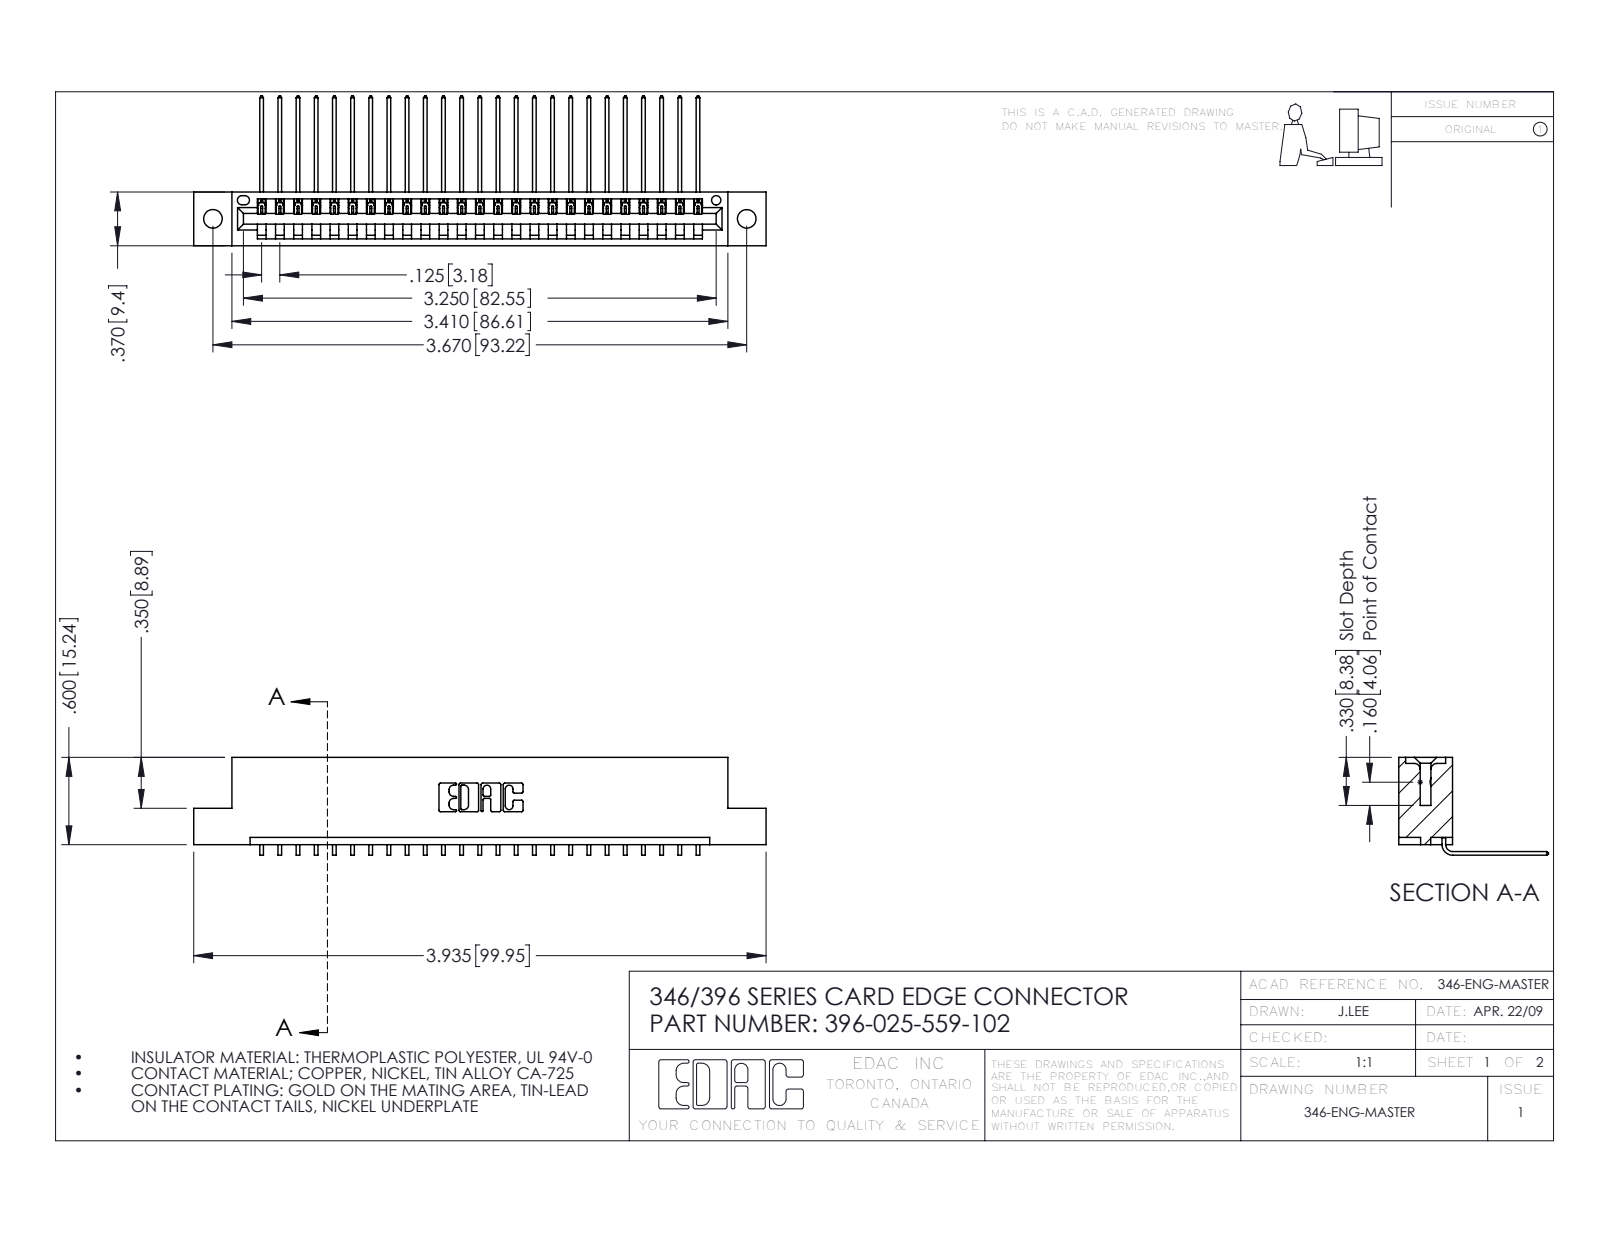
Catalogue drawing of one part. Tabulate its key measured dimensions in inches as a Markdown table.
| quantity | value |
| --- | --- |
| part name | 346 Part_Flush Mounting Lugs - 0.128 Dia; 396-025-559-102; 345-292-001_558 559 Tail - 1 |
| STEP written by | SolidWorks 2016 (CONFIG_CONTROL_DESIGN) |
| units | inches |
| bodies | 26 solids, 1622 faces (1126 planar, 496 cylindrical, 0 other) |
| overall size | 3.935 × 1.03 × 0.673 |
| volume | 0.58 in³ |
| surface area | 18.46 in² |
| round holes (diameter × count) | 0.128 × 2, 0.064 × 1 |
| partial cylindrical surfaces (radius × count) | 0.006 × 50, 0.01 × 22, 0.007 × 6, 0.031 × 6, 0.026 × 3, 0.031 × 2, 0.04 × 2, 0.014 × 1 |
| main face-to-face distances | 0.048, 0.322, 0.37, 0.25, 0.072, 0.025, 0.298, 0.148, 0.222, 0.1 |
| hole center spacings | 0.246, 3.462, 3.67 |
